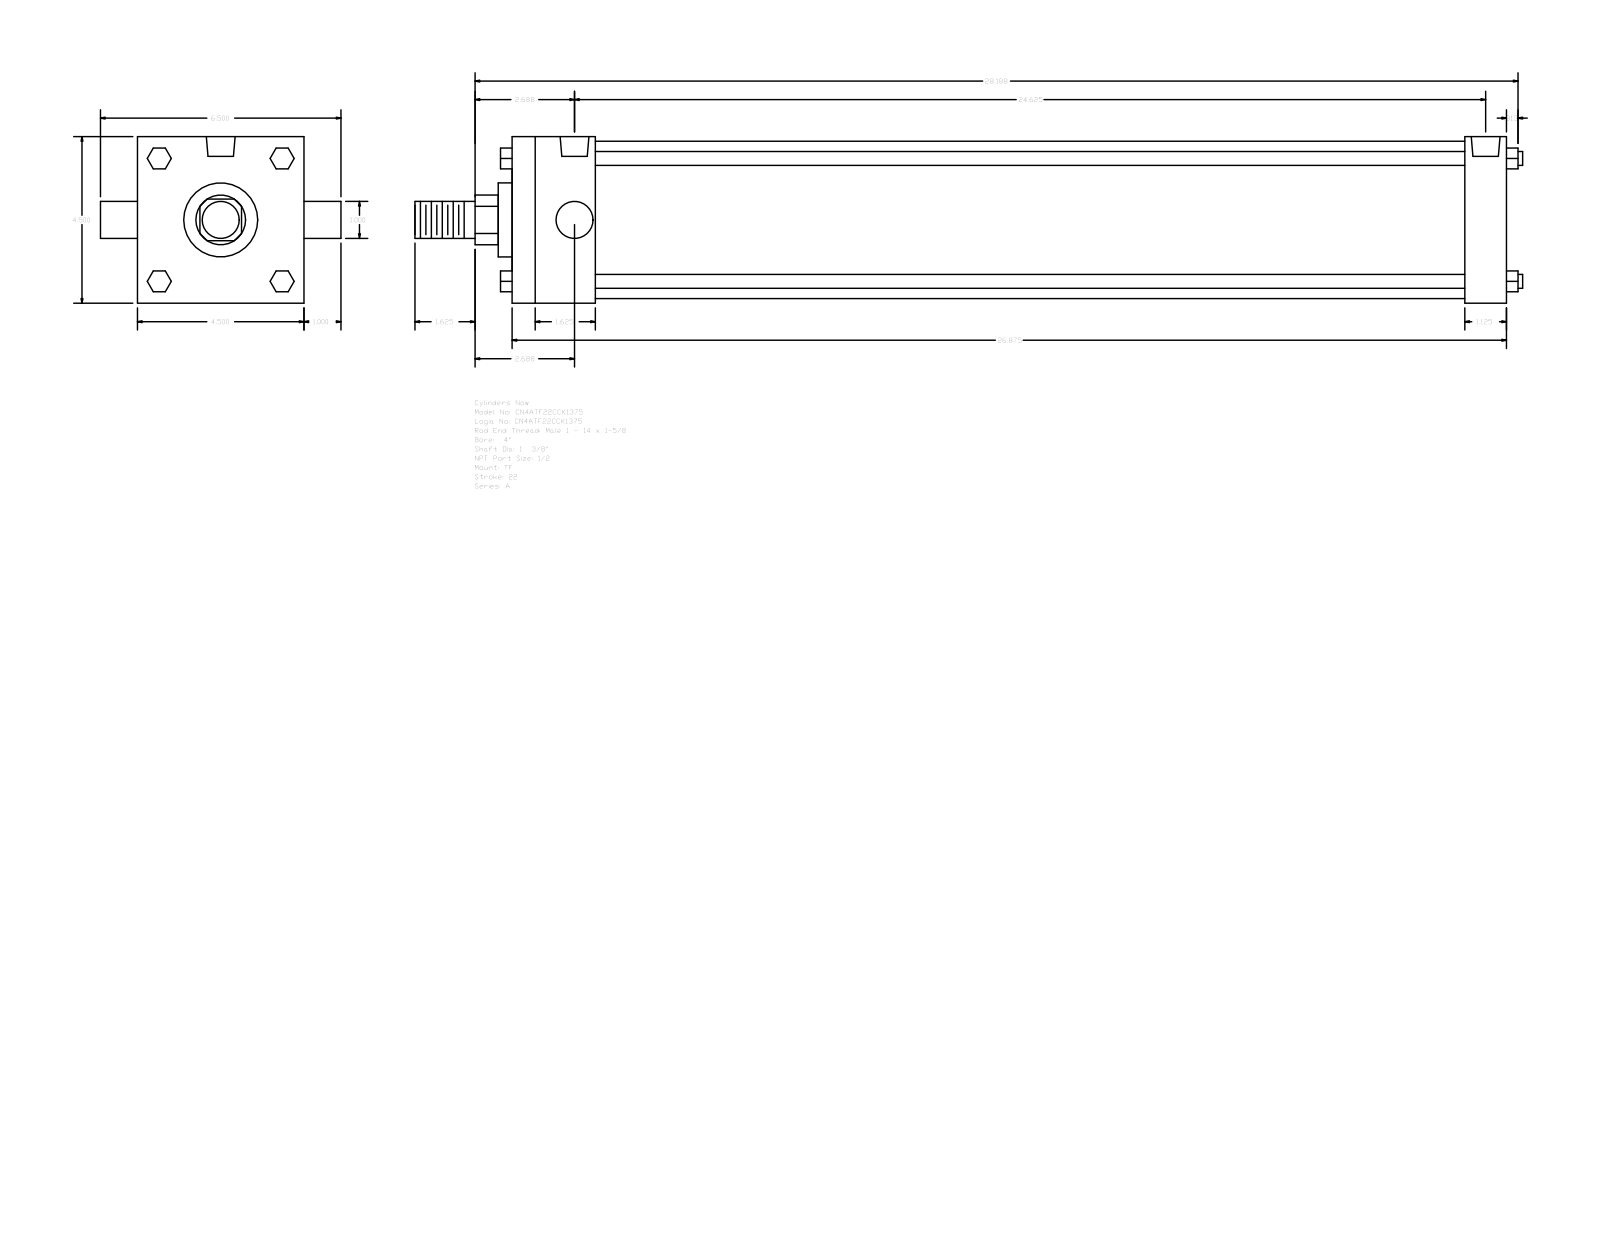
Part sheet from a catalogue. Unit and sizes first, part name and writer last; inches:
Units: inches
Overall size (bounding box): 29.937 × 6.5 × 4.5
Round holes (diameter × count): ⌀0.344 ×3, ⌀0.778 ×2
Round bosses / shafts (diameter × count): ⌀0.375 ×4, ⌀1 ×2, ⌀4.25 ×1, ⌀2 ×1, ⌀1.375 ×1
Partial cylindrical surfaces — rounded edges, fillets, slot ends (radius × count): R0.672 ×1
Main face-to-face distances: 4.5, 26.875, 2.25, 25.75, 1.125, 23.5, 24.625, 2.625, 0.563, 1
Hole centre spacings: 0.125, 24.5, 24.375, 24.625
Bodies: 0 solids, 120 faces (92 planar, 28 cylindrical, 0 other)
Part name (STEP PRODUCT): A_TF__0400_1.375
STEP written by: GSSL Pune (CONFIG_CONTROL_DESIGN)
